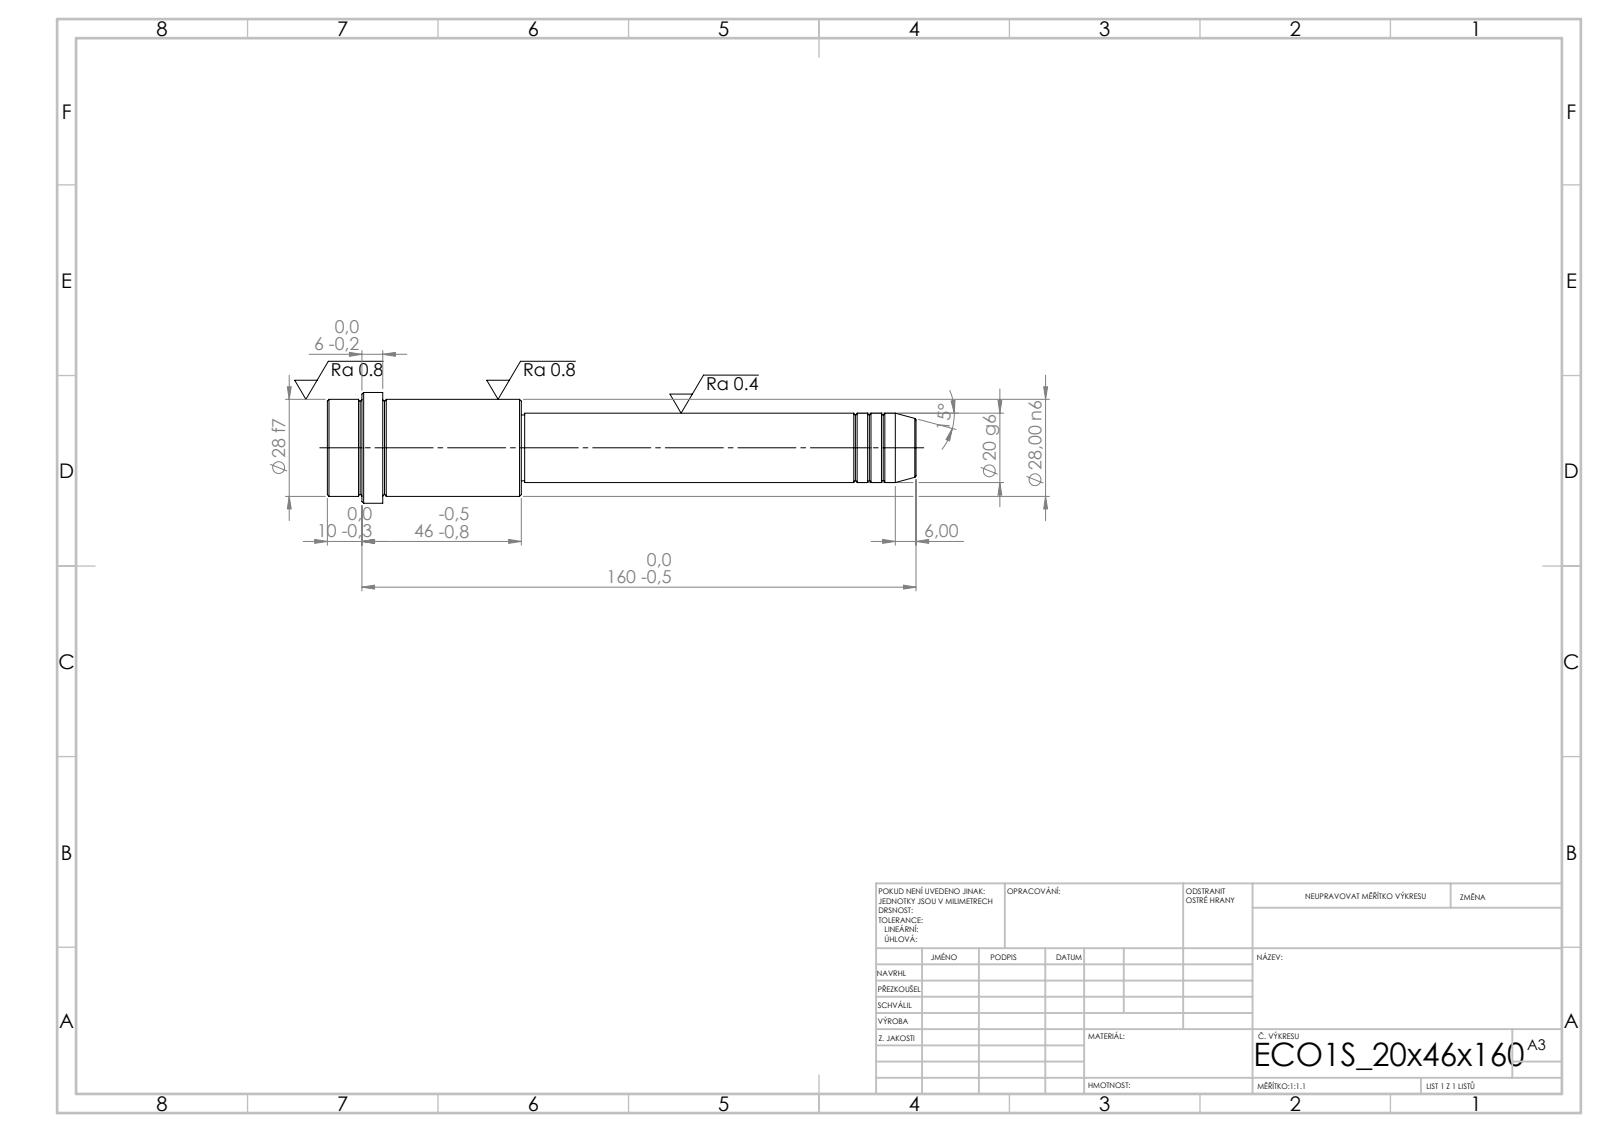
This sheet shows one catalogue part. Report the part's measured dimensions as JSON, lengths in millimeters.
{"step_written_by": "SolidWorks 2019 (CONFIG_CONTROL_DESIGN)", "units": "millimeters", "bodies": {"solids": 1, "faces": 52, "planar": 6, "cylindrical": 16, "other": 30}, "overall_size": [170, 32, 32], "volume_mm3": 70934, "surface_area_mm2": 13824, "round_bosses_or_shafts": [[32, 1], [28, 1], [20, 1], [19, 1]], "face_to_face_distances": [56, 114, 170, 154, 40, 16, 160, 46, 6, 10]}
